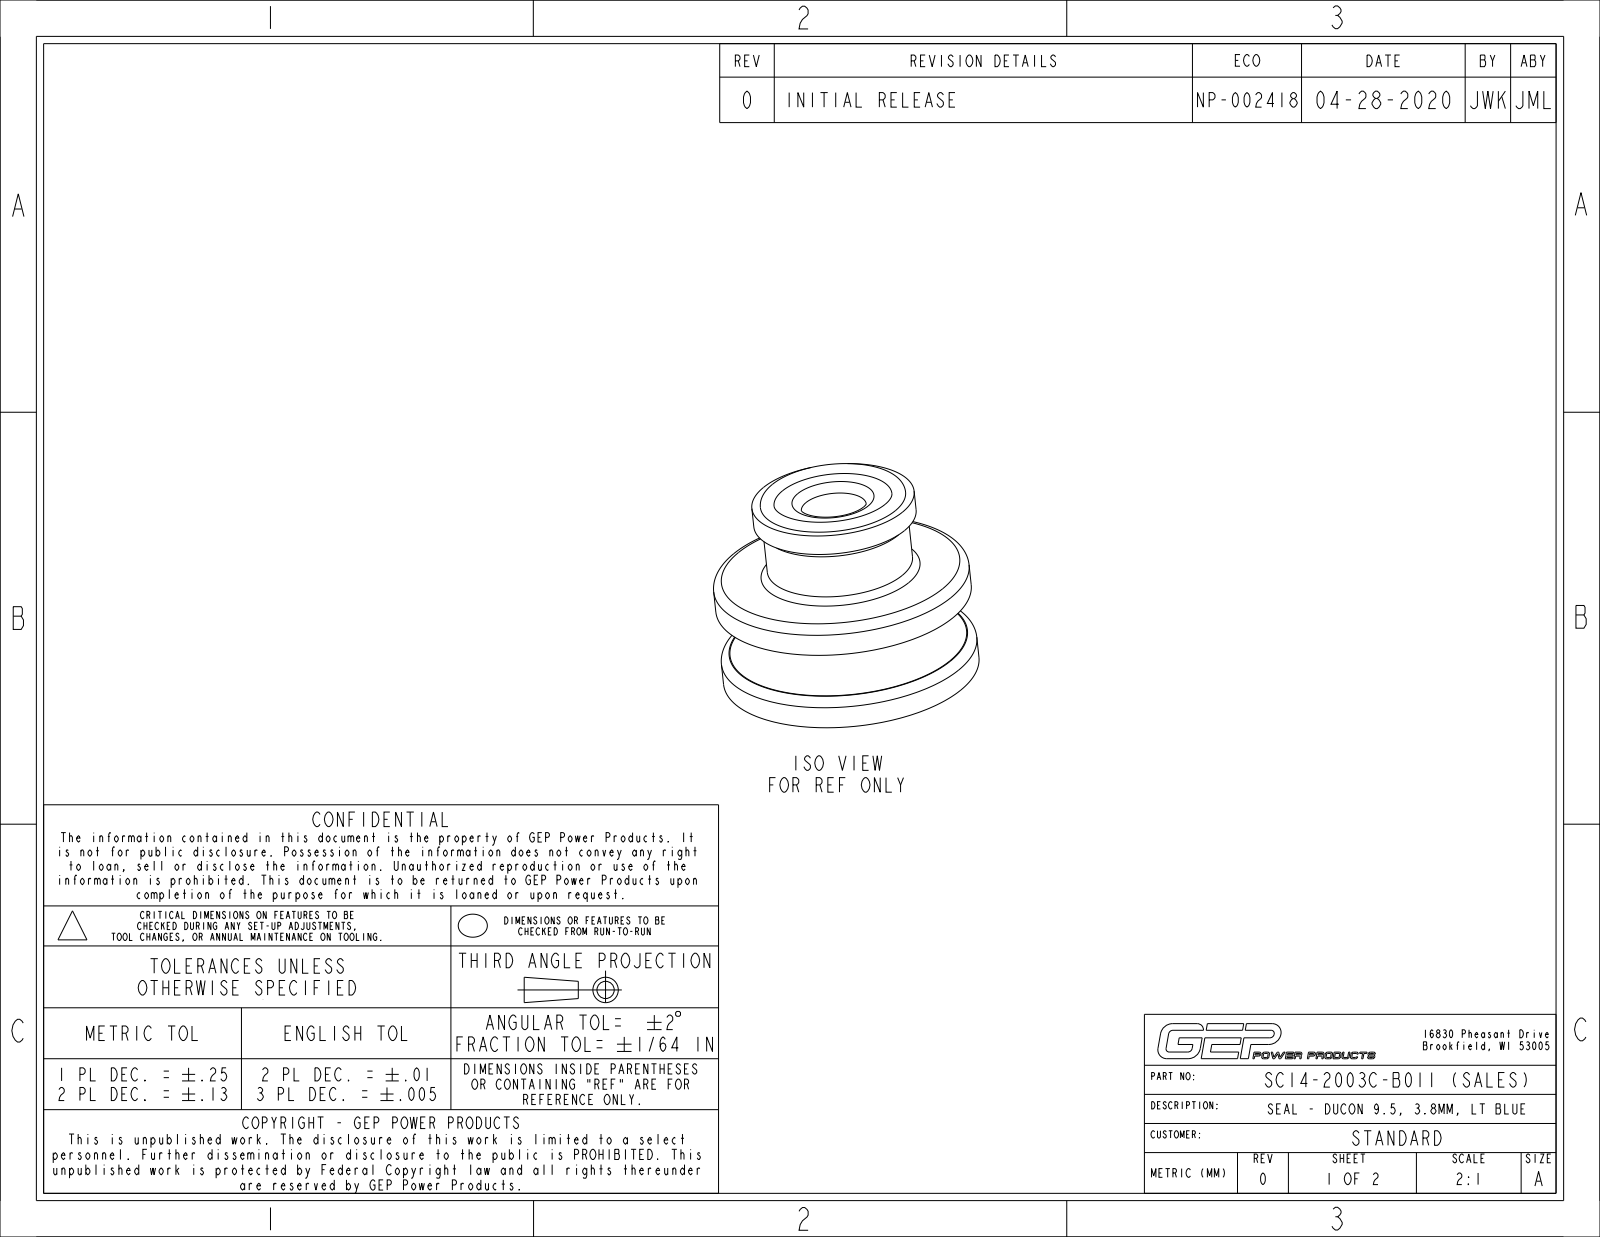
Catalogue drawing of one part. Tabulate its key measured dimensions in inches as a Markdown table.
| quantity | value |
| --- | --- |
| part name | PC14-2003C-B011_NCF; SC14-2003C-B011_NCF_ASM |
| STEP written by | CREO PARAMETRIC BY PTC INC, 2017110 (CONFIG_CONTROL_DESIGN) |
| units | inches |
| bodies | 1 solid, 88 faces (42 planar, 10 cylindrical, 36 other) |
| overall size | 0.589 × 0.589 × 0.476 |
| volume | 0.067 in³ |
| surface area | 1.581 in² |
| round holes (diameter × count) | 0.15 × 1 |
| round bosses / shafts (diameter × count) | 0.589 × 1, 0.374 × 1, 0.335 × 1 |
| main face-to-face distances | 0.256, 0.437, 0.181, 0.071, 0.185, 0.252, 0.39, 0.205, 0.134, 0.047 |
